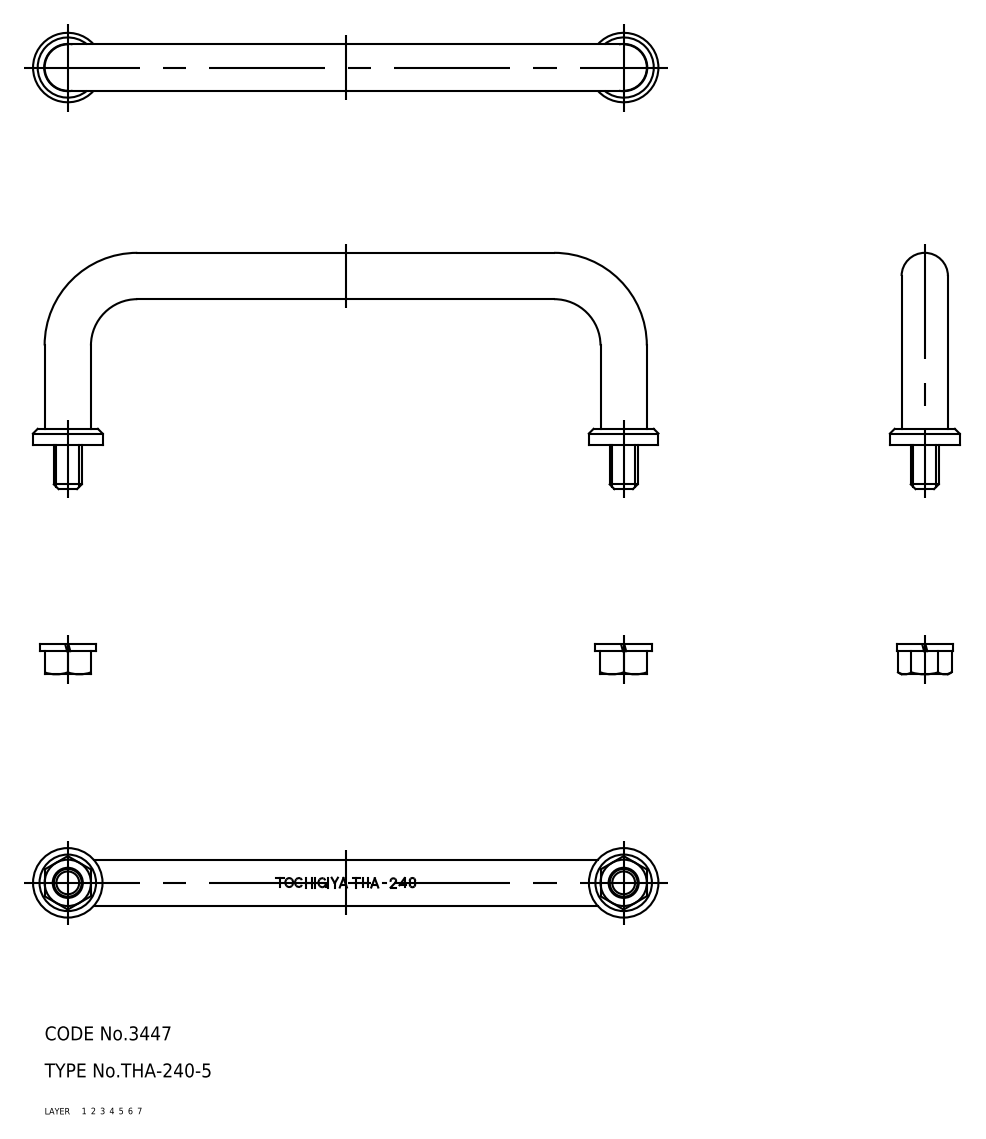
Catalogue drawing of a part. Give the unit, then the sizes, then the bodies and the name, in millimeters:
Units: millimetres
Overall size (bounding box): 135 × 51 × 15
Volume: 16 191 mm³ · Surface area: 8 437 mm²
Bodies: 7 solids, 80 faces (0 planar, 0 cylindrical, 80 other)
Part name (STEP PRODUCT): facing ring; nut; washer; pull (+1 more)
STEP written by: CADfix (AUTOMOTIVE_DESIGN)
